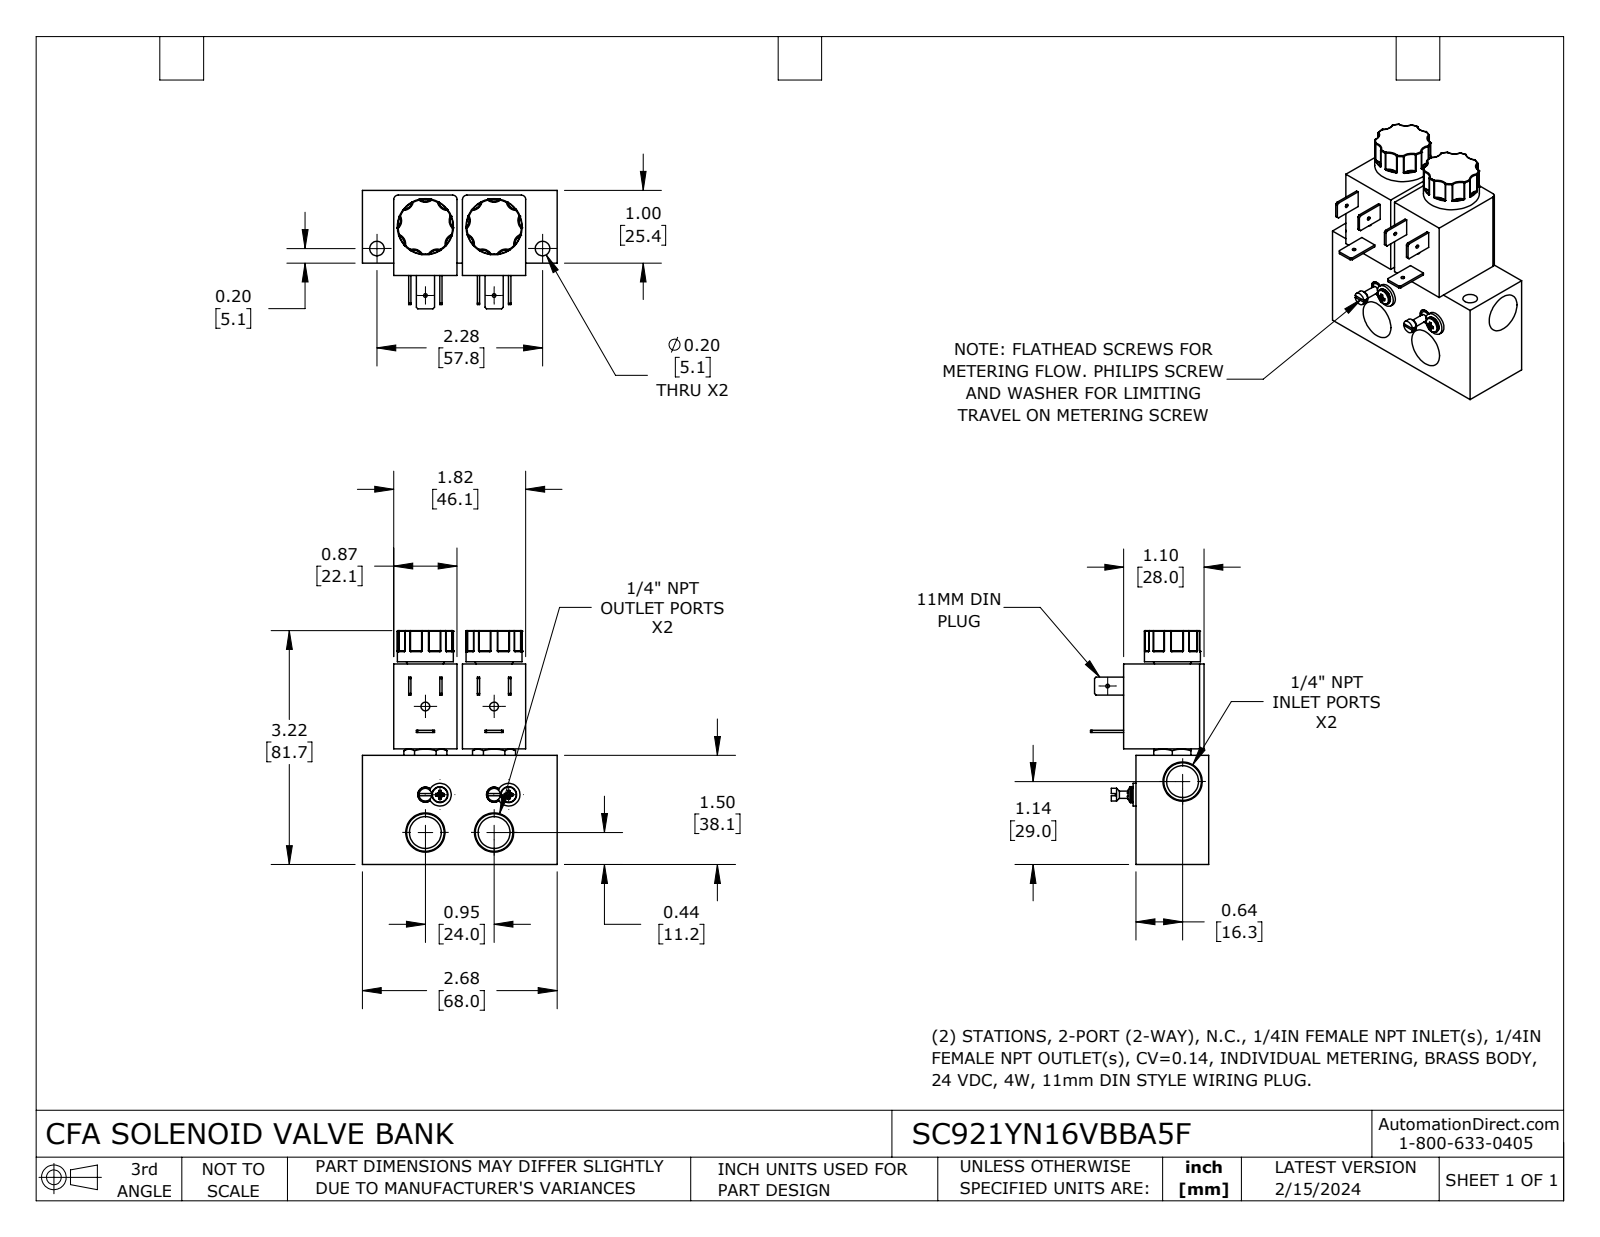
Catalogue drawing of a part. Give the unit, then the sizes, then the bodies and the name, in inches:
Units: inches
Overall size (bounding box): 3.215 × 2.677 × 1.627
Round holes (diameter × count): ⌀0.05 ×3, ⌀0.438 ×3, ⌀0.12 ×2, ⌀0.2 ×2, ⌀0.208 ×2
Round bosses / shafts (diameter × count): ⌀0.77 ×2, ⌀0.312 ×2, ⌀0.219 ×2, ⌀0.206 ×2, ⌀0.175 ×2, ⌀0.102 ×2, ⌀0.1 ×2
Partial cylindrical surfaces — rounded edges, fillets, slot ends (radius × count): R0.01 ×36, R0.133 ×18, R0.06 ×4, R0.308 ×1
Main face-to-face distances: 1, 0.945, 0.431, 1.301, 1.376, 2.246, 0.87, 1.5, 1.169, 0.169
Hole centre spacings: 0.945, 0.52, 0.928, 1.078, 1.212, 1.537, 1.732, 1.735
Volume: 6.159 in³ · Surface area: 40.27 in²
Bodies: 1 solid, 589 faces (156 planar, 152 cylindrical, 281 other)
Part name (STEP PRODUCT): SC921YN16VBBA5F
STEP written by: SolidWorks 2023 (CONFIG_CONTROL_DESIGN)
